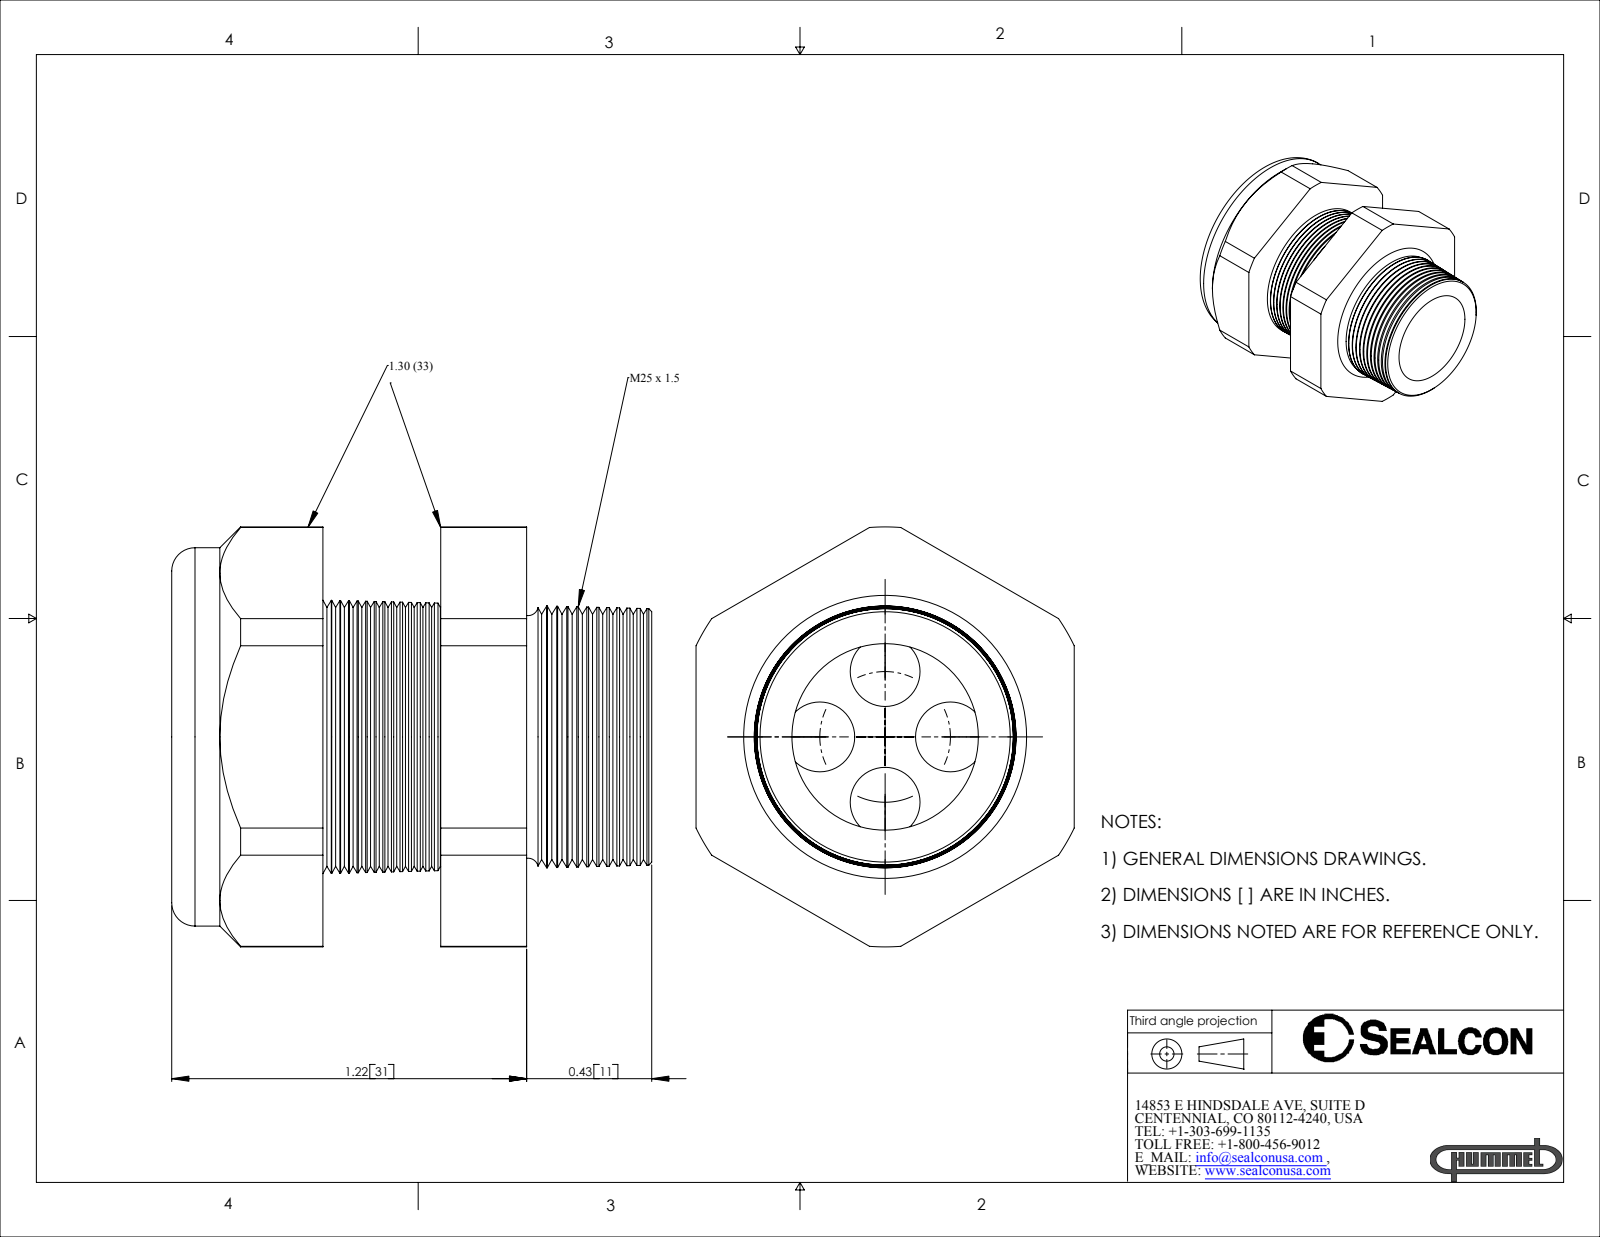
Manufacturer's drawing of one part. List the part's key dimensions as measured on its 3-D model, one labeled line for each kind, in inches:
Part name (STEP PRODUCT): CD25M1-GY
STEP written by: SolidWorks 2007 (CONFIG_CONTROL_DESIGN)
Units: inches
Bodies: 2 solids, 214 faces (20 planar, 28 cylindrical, 166 other)
Overall size (bounding box): 1.65 × 1.443 × 1.3
Volume: 1.131 in³ · Surface area: 17.19 in²
Round holes (diameter × count): ⌀0.24 ×4, ⌀0.69 ×1, ⌀0.71 ×1
Round bosses / shafts (diameter × count): ⌀1.3 ×1
Partial cylindrical surfaces — rounded edges, fillets, slot ends (radius × count): R0.721 ×1
Main face-to-face distances: 1.3, 0.405, 0.7, 0.295, 0.52, 0.925, 1.22, 1.65, 1.13, 0.725
Hole centre spacings: 0.224, 0.317, 0.449
